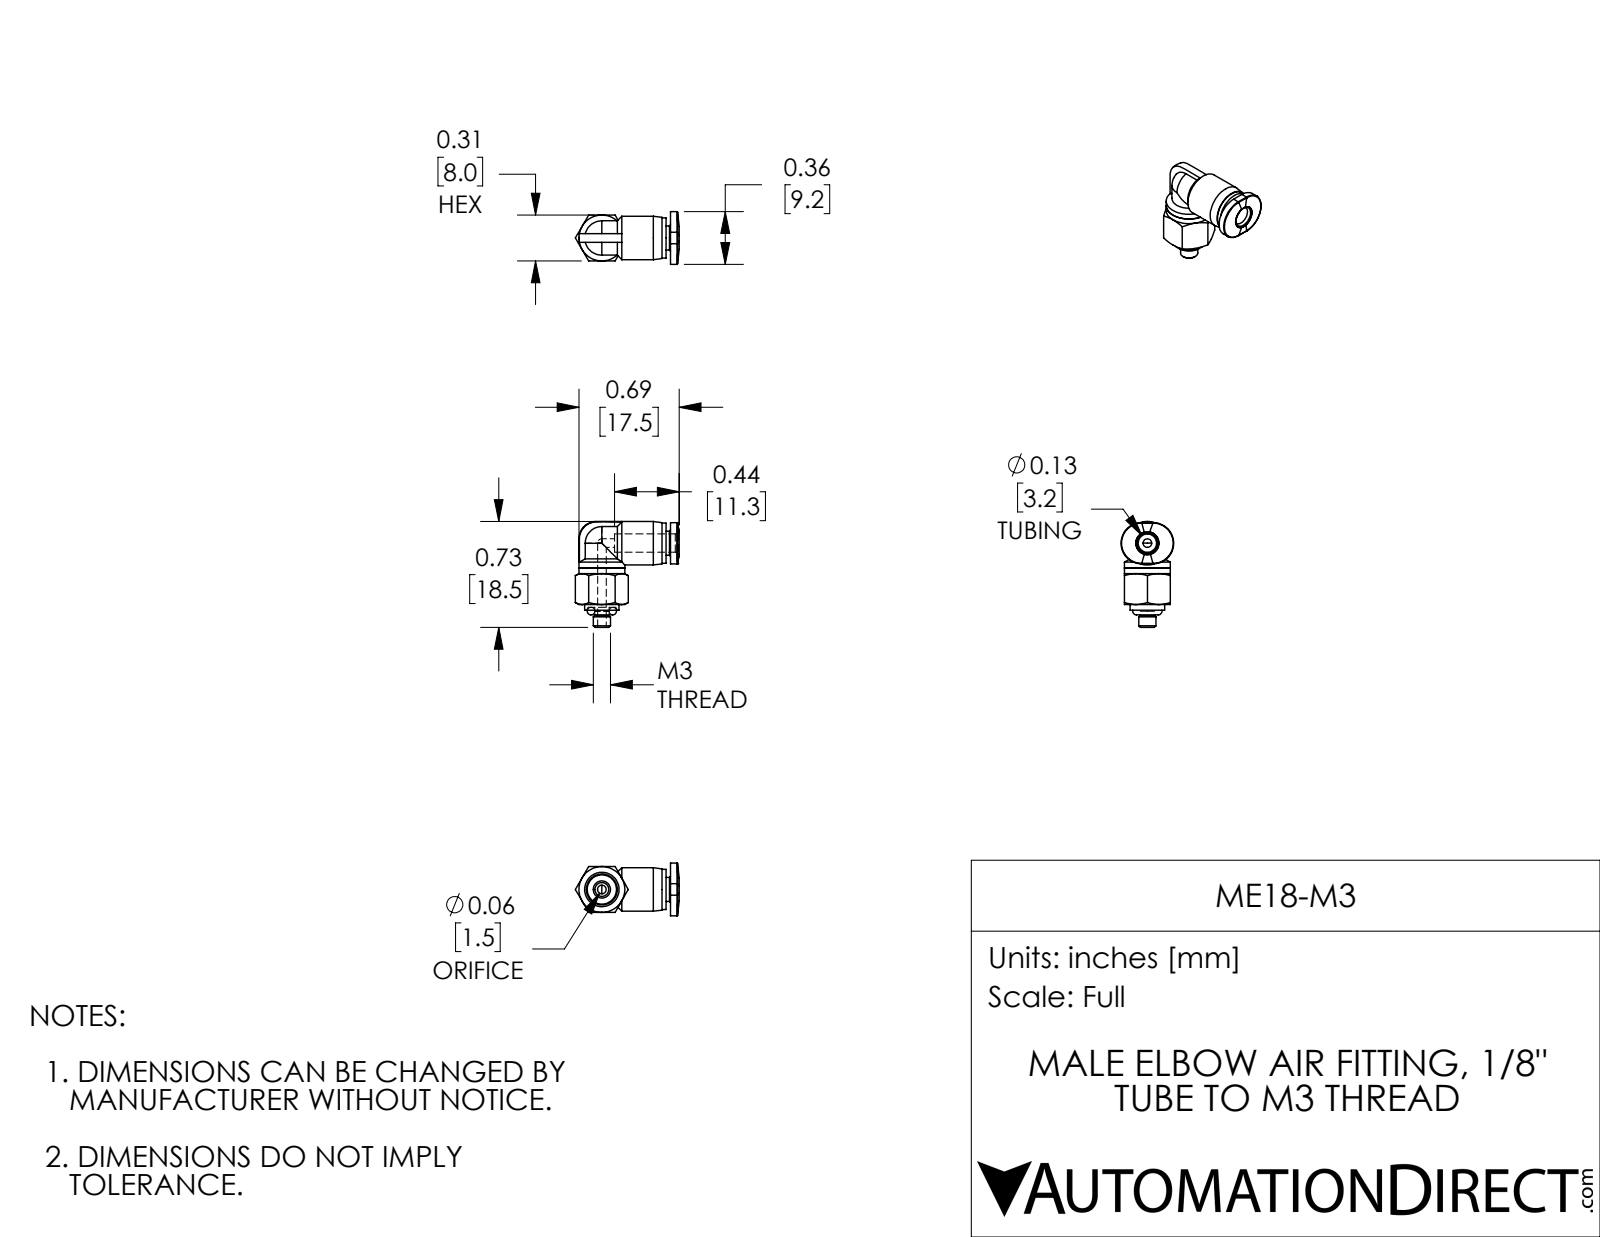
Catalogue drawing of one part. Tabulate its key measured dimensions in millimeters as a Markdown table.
| quantity | value |
| --- | --- |
| part name | ME18-M3 |
| STEP written by | SolidWorks 2018 (AUTOMOTIVE_DESIGN) |
| units | millimeters |
| bodies | 2 solids, 106 faces (22 planar, 32 cylindrical, 52 other) |
| overall size | 18.5 × 18.1 × 9.2 |
| volume | 970 mm³ |
| surface area | 1 093 mm² |
| round holes (diameter × count) | 1.5 × 2, 3.2 × 1 |
| round bosses / shafts (diameter × count) | 8 × 1, 7.6 × 1, 7 × 1, 6.2 × 1, 6 × 1, 4.2 × 1, 3 × 1, 2.5 × 1 |
| partial cylindrical surfaces (radius × count) | 3.6 × 2, 3 × 1 |
| main face-to-face distances | 8, 0.8, 3.3, 4.7, 6.4, 0.5, 1.5, 6.9, 9, 9.8 |
